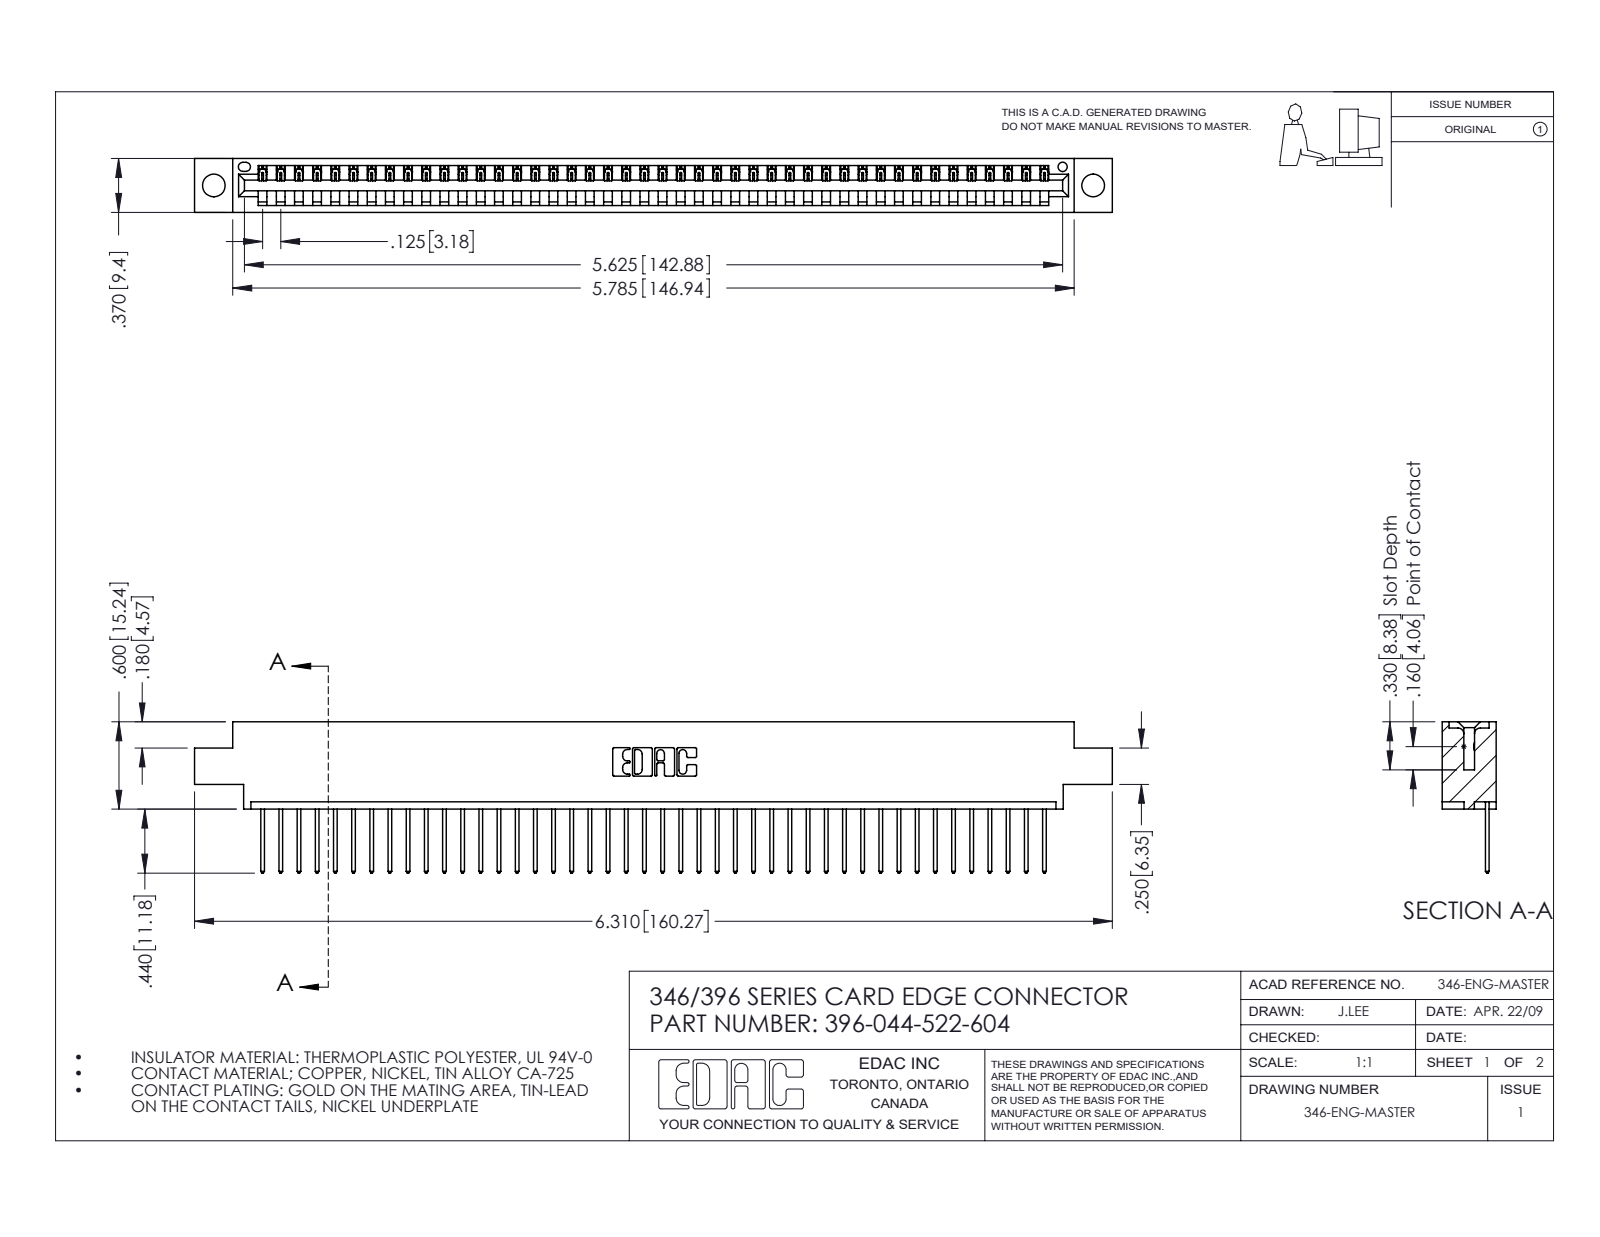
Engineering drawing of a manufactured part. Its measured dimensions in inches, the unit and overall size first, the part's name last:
Units: inches
Overall size (bounding box): 6.31 × 1.04 × 0.37
Round holes (diameter × count): ⌀0.156 ×2, ⌀0.064 ×1
Partial cylindrical surfaces — rounded edges, fillets, slot ends (radius × count): R0.006 ×88, R0.01 ×88, R0.01 ×22, R0.007 ×6, R0.031 ×6, R0.026 ×3, R0.031 ×2, R0.04 ×2
Main face-to-face distances: 0.048, 0.322, 0.37, 0.25, 0.072, 0.298, 0.025, 0.148, 0.222, 0.1
Hole centre spacings: 0.246, 5.836, 6.045
Volume: 0.923 in³ · Surface area: 29.52 in²
Bodies: 45 solids, 2678 faces (1840 planar, 838 cylindrical, 0 other)
Part name (STEP PRODUCT): 396-044-522-604; 345-292-001_345-293-122; 346 Part_0.170 Offset - 0.156 Dia-TH
STEP written by: SolidWorks 2016 (CONFIG_CONTROL_DESIGN)
